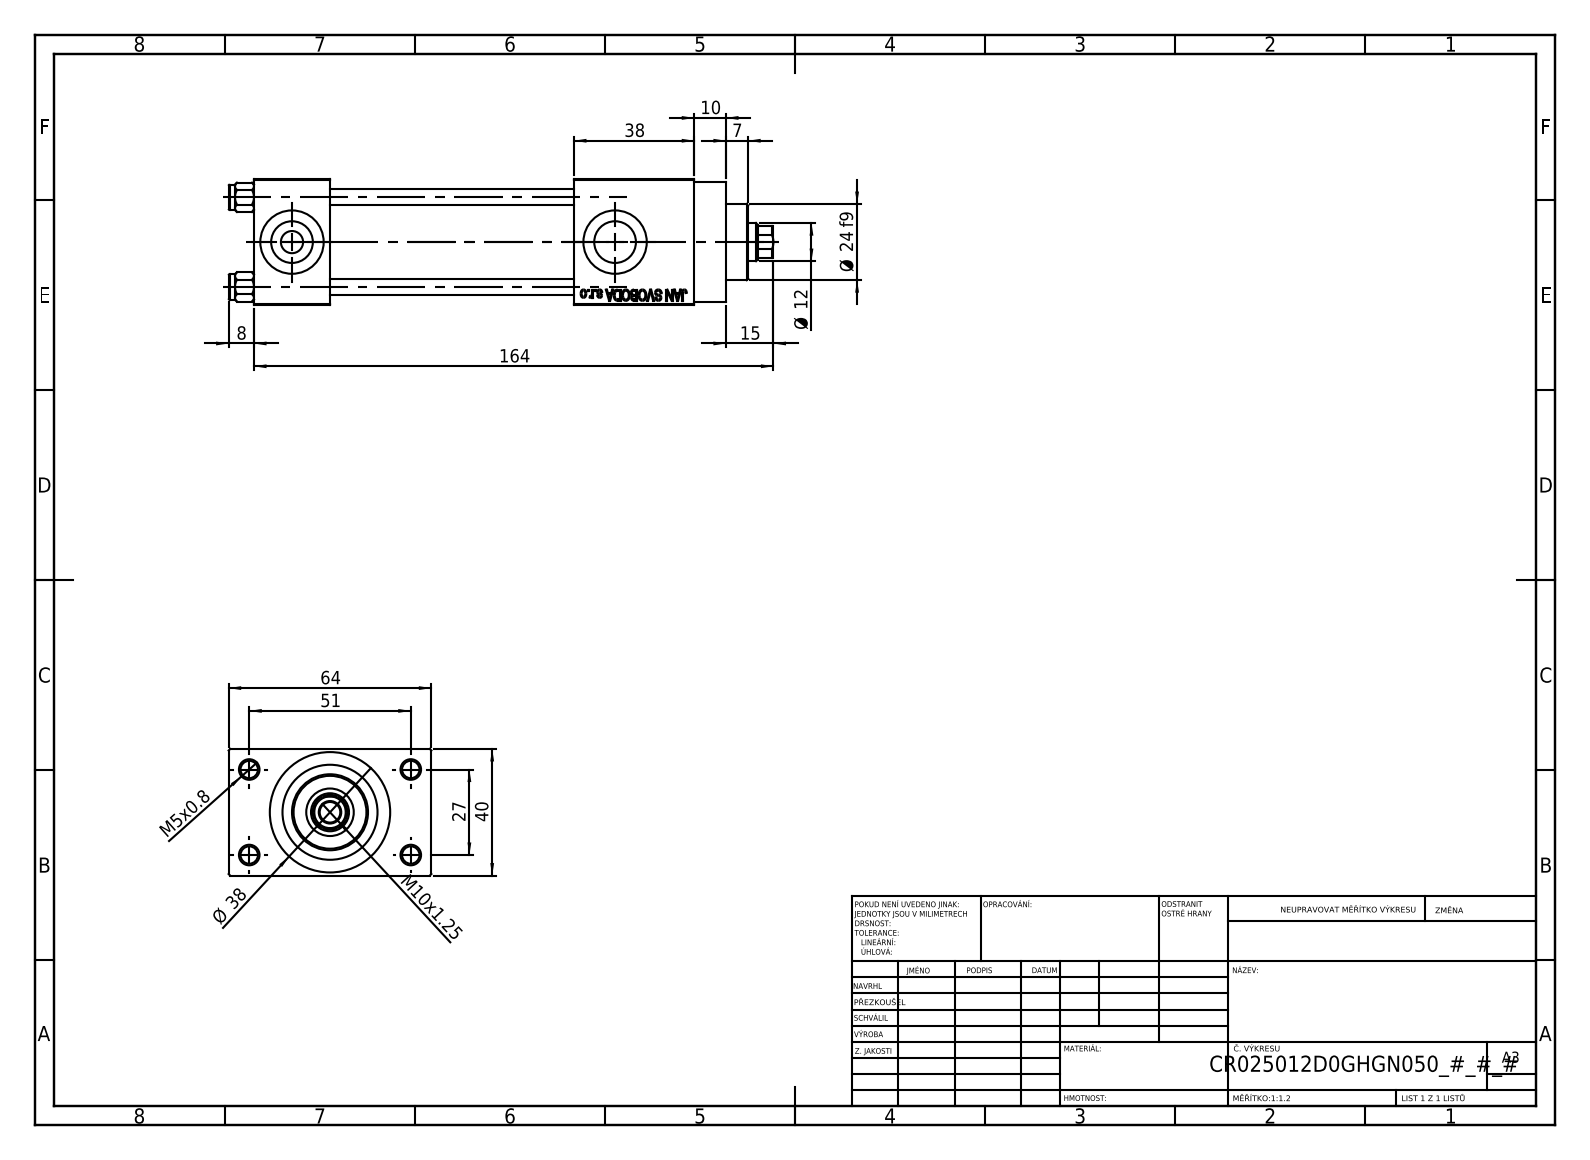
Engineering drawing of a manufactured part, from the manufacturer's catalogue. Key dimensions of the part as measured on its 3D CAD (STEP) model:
Part name (STEP PRODUCT): V215CR_VCP_D; NUT_M5_D; V215CR_D_Body; V215CR_D_TYCINKA (+1 more)
STEP written by: SolidWorks 2019 (CONFIG_CONTROL_DESIGN)
Units: millimetres
Bodies: 11 solids, 1102 faces (496 planar, 88 cylindrical, 518 other)
Overall size (bounding box): 172 × 64 × 40
Volume: 187 349 mm³ · Surface area: 70 454 mm²
Round holes (diameter × count): ⌀5 ×4, ⌀5.5 ×4, ⌀20 ×3, ⌀7 ×2, ⌀13.16 ×2, ⌀6.5 ×1, ⌀12 ×1, ⌀15 ×1, ⌀25 ×1, ⌀30 ×1
Round bosses / shafts (diameter × count): ⌀8 ×4, ⌀38 ×1, ⌀31 ×1, ⌀24 ×1
Partial cylindrical surfaces — rounded edges, fillets, slot ends (radius × count): R5.5 ×1
Main face-to-face distances: 40, 12, 77, 24, 101, 52, 38, 139, 115, 64
Hole centre spacings: 11.37, 20.01, 28.3, 28.85, 29.89, 39.66, 48.34, 27
